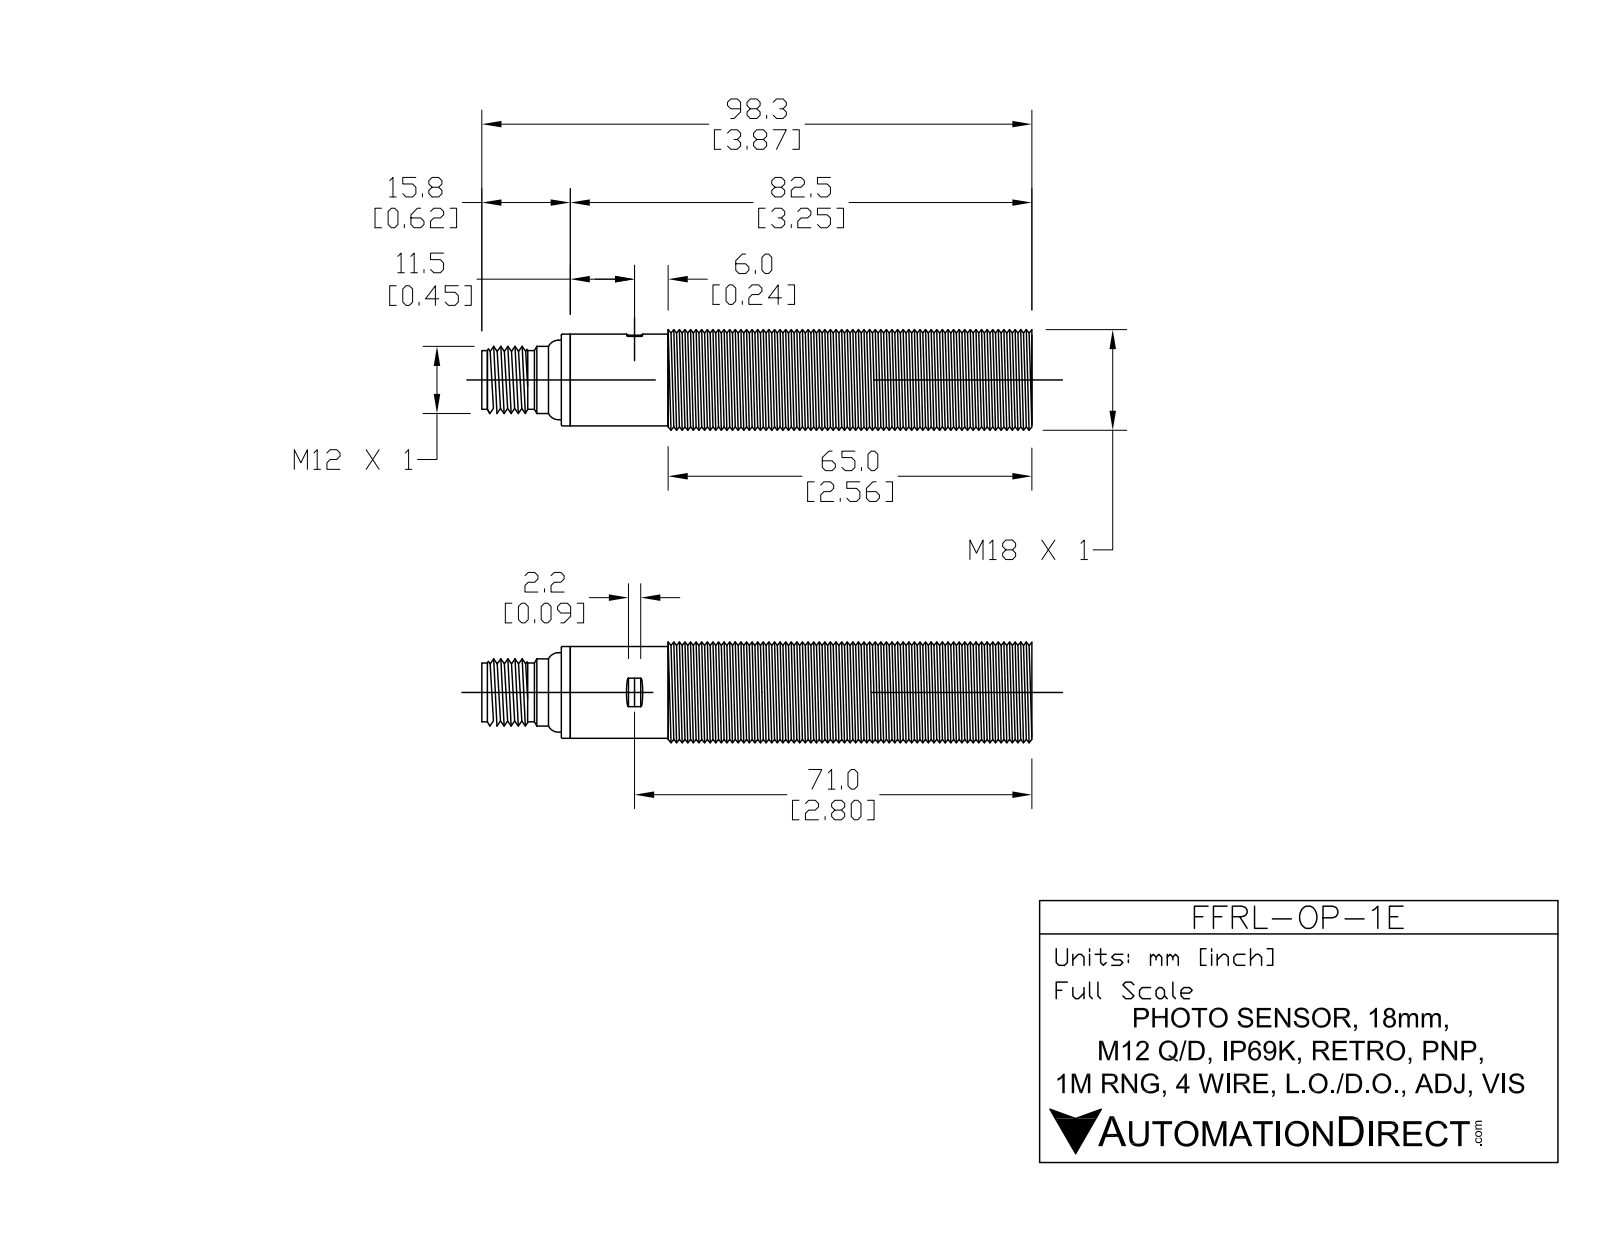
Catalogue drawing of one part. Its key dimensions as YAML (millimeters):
part_name: "FFRL-0P-1E"
step_written_by: "SolidWorks 2017 (AUTOMOTIVE_DESIGN)"
units: millimeters
bodies: {solids: 5, faces: 118, planar: 21, cylindrical: 48, other: 49}
overall_size: [83, 18, 18]
volume: 17710
surface_area: 6755
round_holes:
  - {diameter: 7.1, count: 1}
  - {diameter: 8.3, count: 1}
  - {diameter: 12.7, count: 1}
  - {diameter: 14.8, count: 1}
  - {diameter: 15.5, count: 1}
round_bosses_or_shafts:
  - {diameter: 1, count: 4}
  - {diameter: 18, count: 1}
  - {diameter: 16.4, count: 1}
  - {diameter: 15.5, count: 1}
  - {diameter: 15.3, count: 1}
  - {diameter: 14.2, count: 1}
  - {diameter: 12.5, count: 1}
  - {diameter: 12, count: 1}
partial_cylinders:
  - {radius: 0.6, count: 1}
  - {radius: 16, count: 1}
face_to_face_distances: [64.5, 3, 67.5, 0.6, 2.4, 66.9, 69, 68.4, 66, 1.5]
